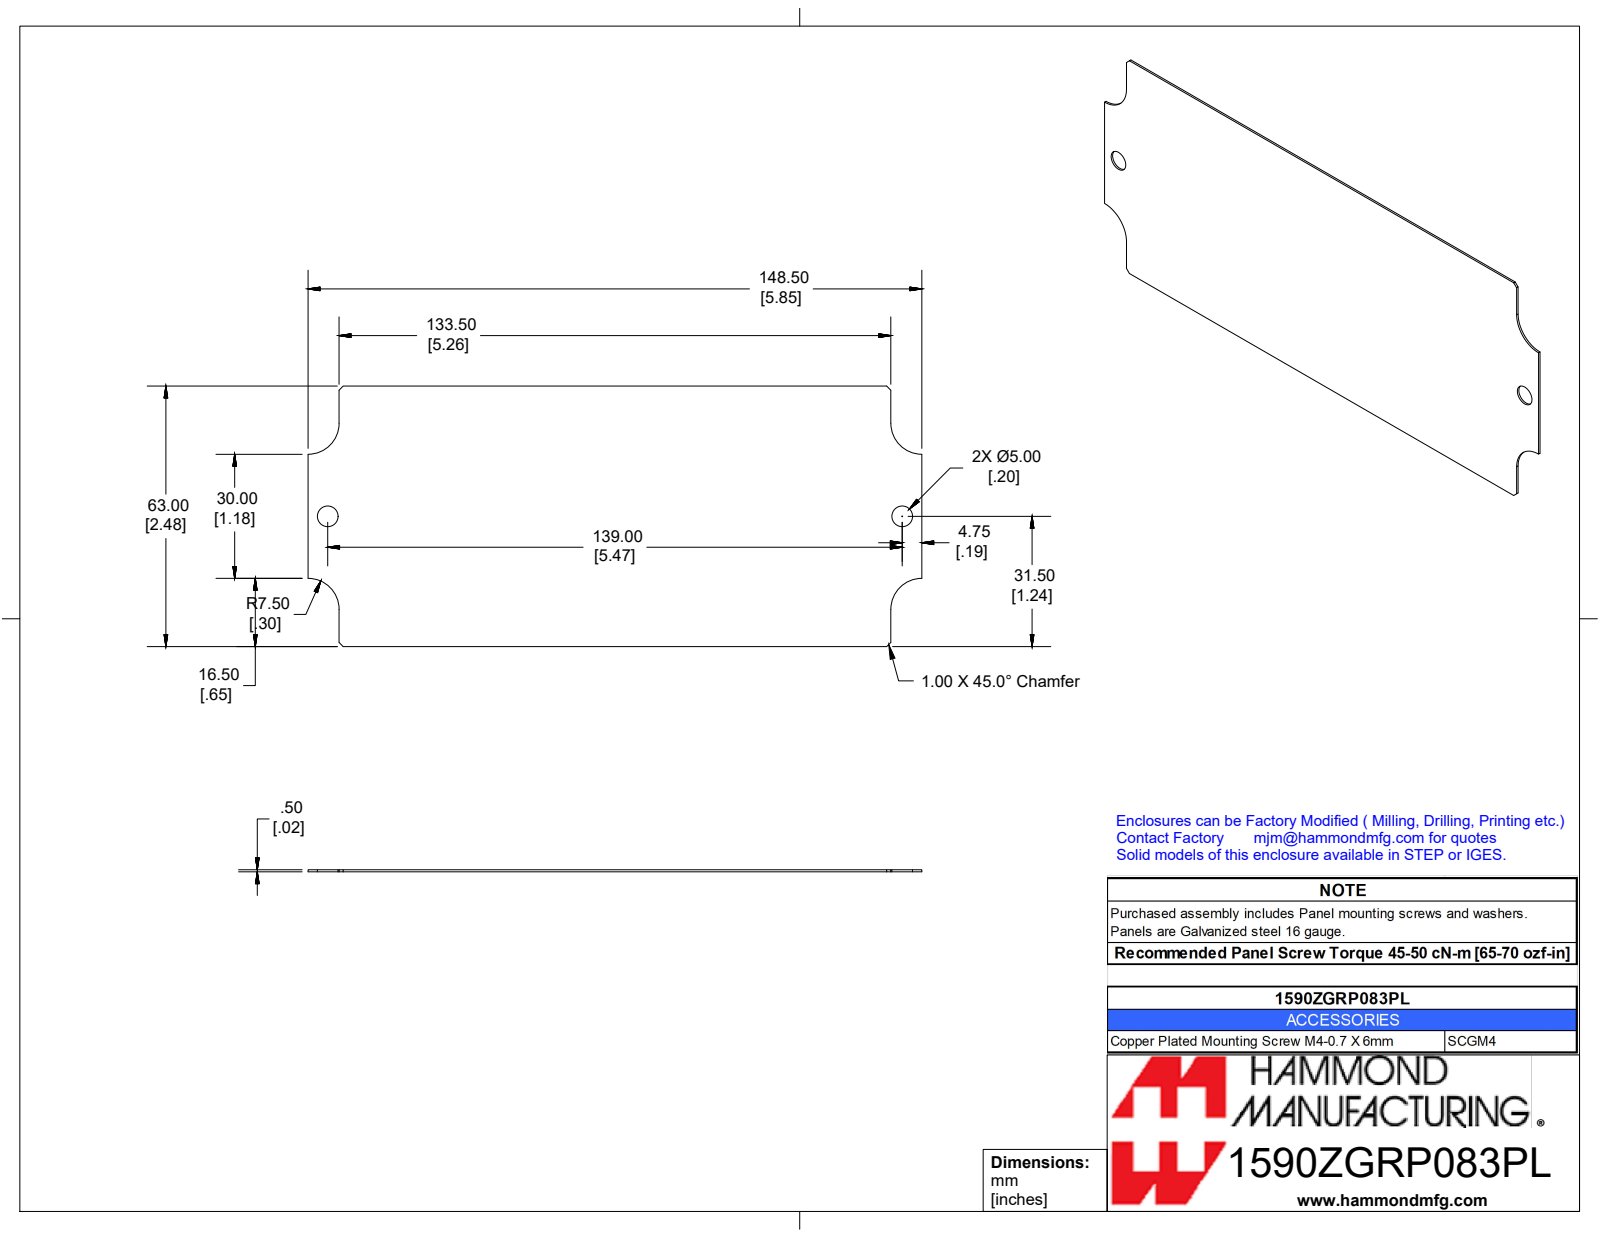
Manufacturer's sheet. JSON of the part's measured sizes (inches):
{"part_name": "1590ZGRP083PL", "step_written_by": "SolidWorks 2019 (CONFIG_CONTROL_DESIGN)", "units": "inches", "bodies": {"solids": 1, "faces": 20, "planar": 14, "cylindrical": 6, "other": 0}, "overall_size": [5.846, 2.48, 0.02], "volume_in3": 0.271, "surface_area_in2": 27.83, "round_holes": [[0.197, 2]], "partial_cylinders_radius": [[0.295, 4]], "face_to_face_distances": [0.02, 2.48, 0.295, 5.551, 5.846, 5.256, 5.414], "hole_center_spacings": [5.472]}
